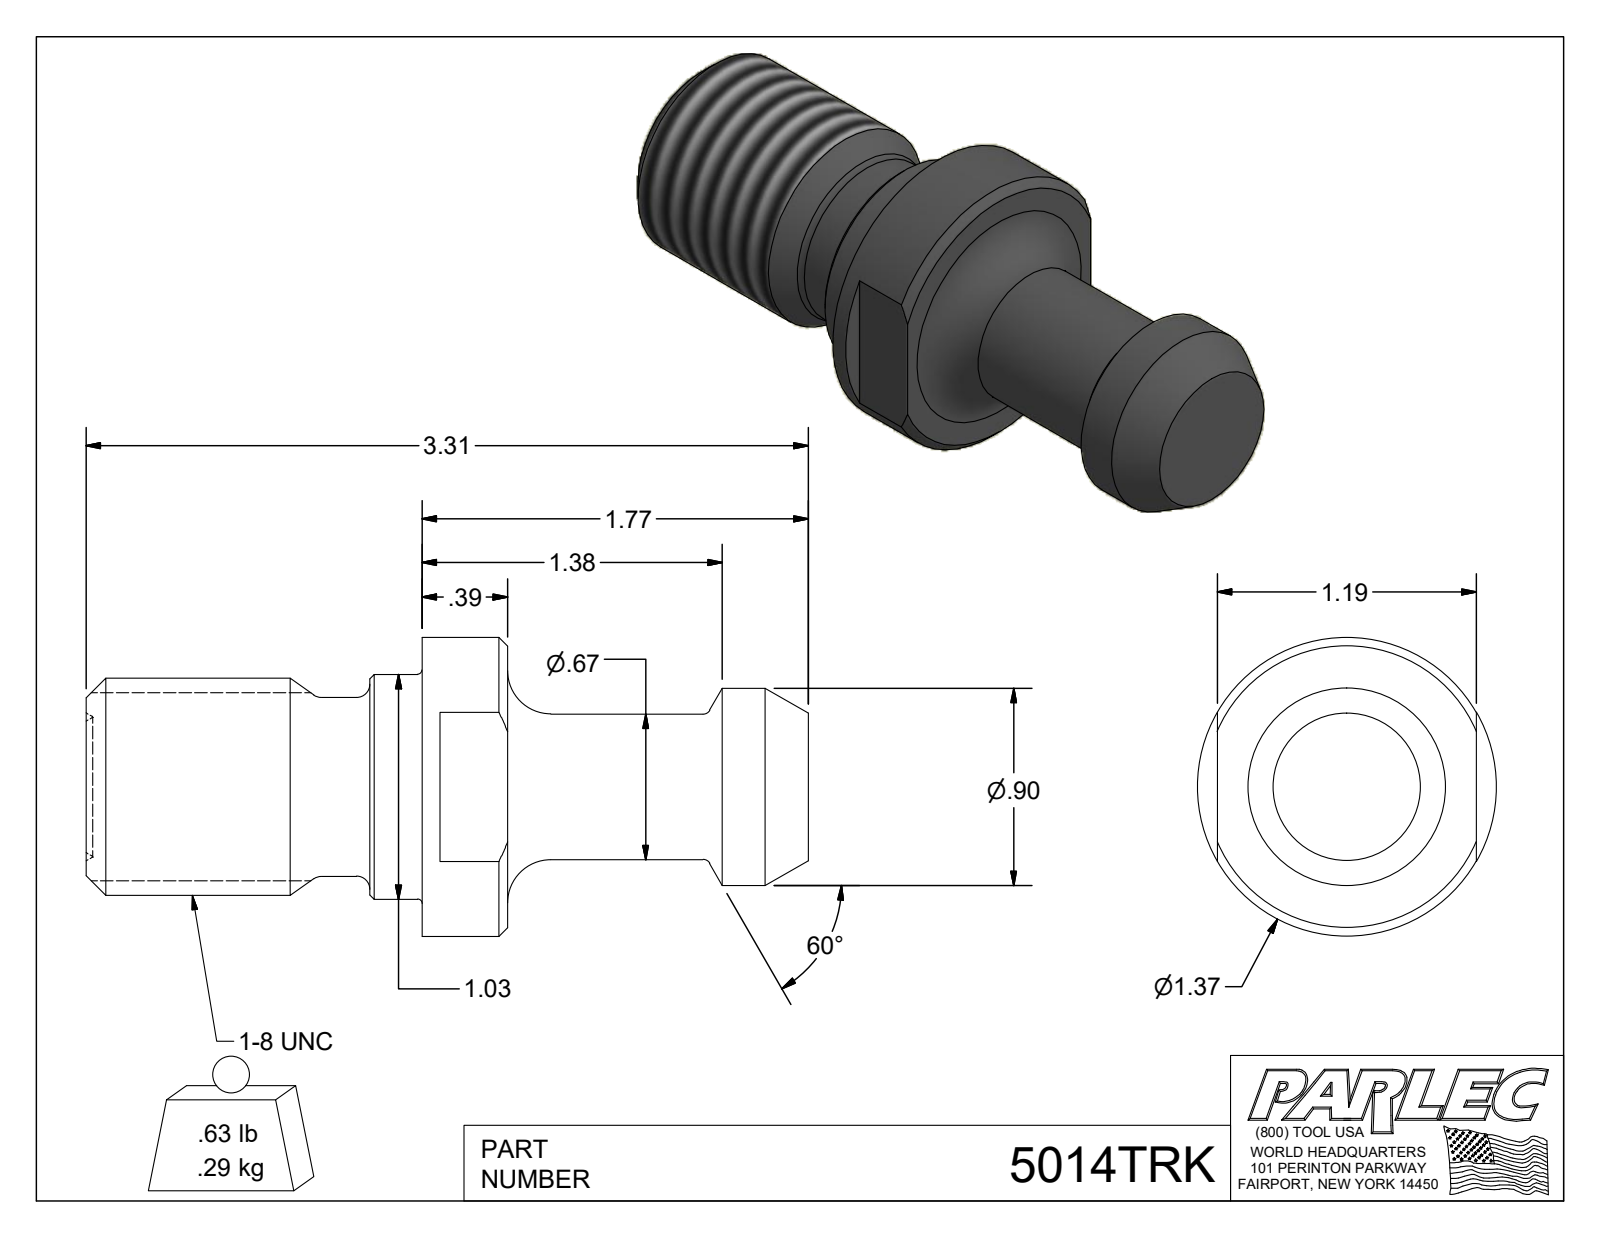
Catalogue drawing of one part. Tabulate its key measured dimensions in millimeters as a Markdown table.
| quantity | value |
| --- | --- |
| part name | 5014TRK |
| STEP written by | Autodesk Inventor 2018 (AUTOMOTIVE_DESIGN) |
| units | millimeters |
| bodies | 1 solid, 31 faces (10 planar, 6 cylindrical, 15 other) |
| overall size | 84.1 × 34.8 × 34.8 |
| volume | 37 200 mm³ |
| surface area | 8 084 mm² |
| round bosses / shafts (diameter × count) | 34.8 × 1, 26.2 × 1, 25.3 × 1, 23 × 1, 20.8 × 1, 16.9 × 1 |
| main face-to-face distances | 39.1, 49.1, 10, 84.1, 45, 35, 30.1, 41.2, 2.1, 7.9 |
